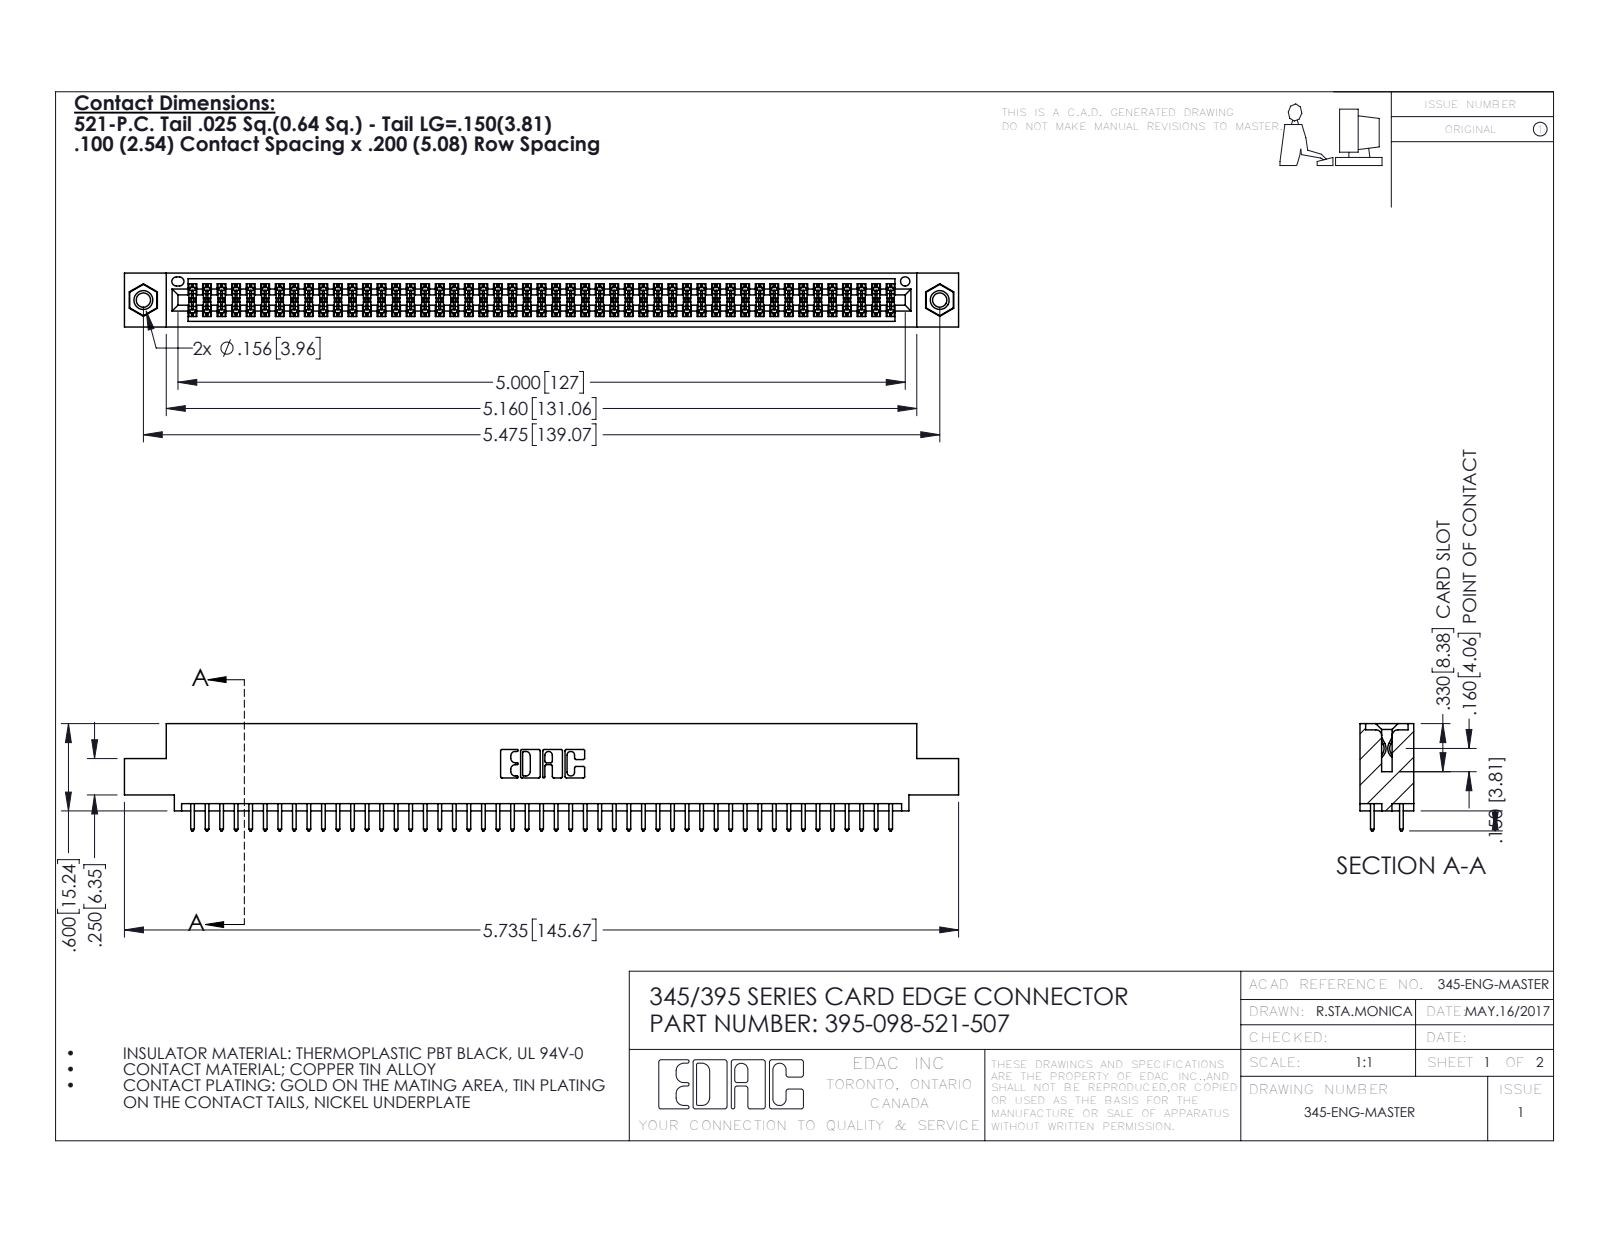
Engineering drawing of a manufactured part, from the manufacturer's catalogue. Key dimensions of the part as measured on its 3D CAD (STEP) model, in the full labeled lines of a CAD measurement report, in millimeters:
Part name (STEP PRODUCT): 345-250-001_345-250-005-103; 395-098-521-507; 345 Part_0.110 Offset - 0.156 Dia-TI; 345-292-001_345-293-121
STEP written by: SolidWorks 2016 (CONFIG_CONTROL_DESIGN)
Units: millimetres
Bodies: 101 solids, 5090 faces (3350 planar, 1724 cylindrical, 16 other)
Overall size (bounding box): 145.7 × 18.7 × 9.4
Volume: 14 100 mm³ · Surface area: 20 820 mm²
Round holes (diameter × count): ⌀2.5 ×2, ⌀3.2 ×2, ⌀4 ×2, ⌀1.6 ×1
Round bosses / shafts (diameter × count): ⌀3.9 ×2
Partial cylindrical surfaces — rounded edges, fillets, slot ends (radius × count): R0.2 ×147, R0.3 ×98, R0.3 ×22, R0.2 ×6, R0.8 ×6, R0.7 ×3, R0.4 ×2, R0.5 ×2
Main face-to-face distances: 1.8, 7.6, 5.1, 9.4, 2.5, 6.9, 0.6, 5.7, 4.4, 3.8
Hole centre spacings: 6.9, 133.1, 139.1
